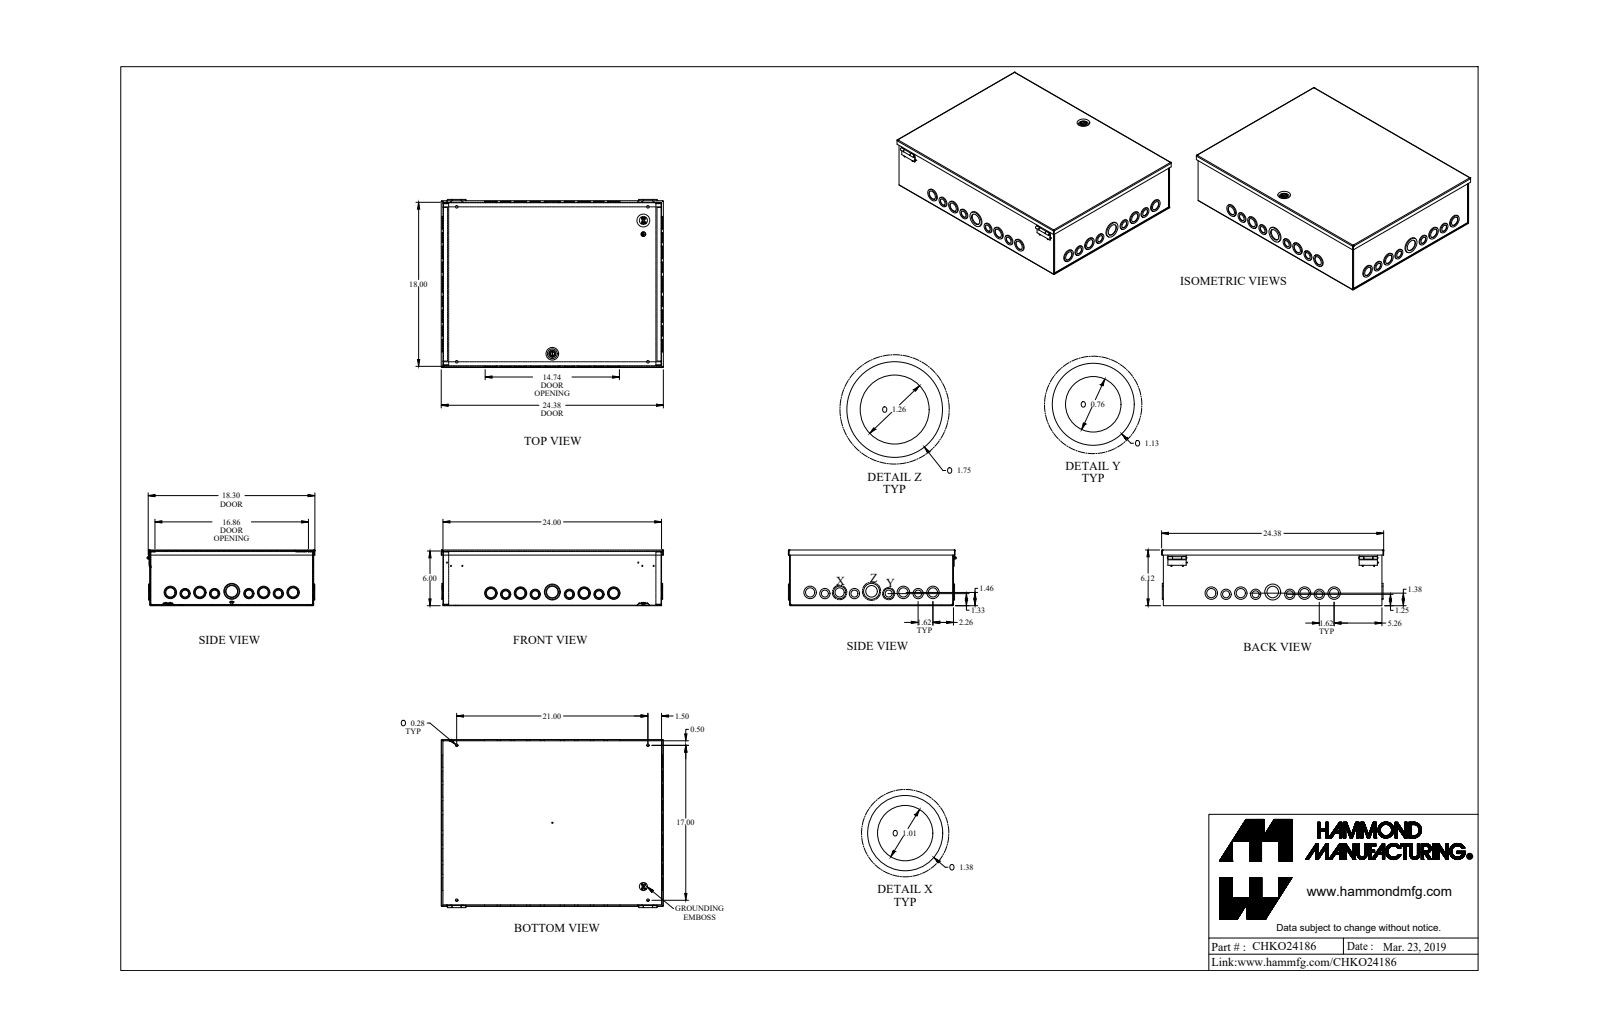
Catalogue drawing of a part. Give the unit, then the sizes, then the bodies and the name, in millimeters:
Units: millimetres
Overall size (bounding box): 619.3 × 468.5 × 155.4
Round holes (diameter × count): ⌀25.7 ×16, ⌀32 ×10, ⌀19.3 ×8, ⌀7.1 ×4, ⌀41.6 ×2, ⌀3.2 ×1, ⌀4.3 ×1, ⌀8.1 ×1, ⌀12.1 ×1, ⌀12.7 ×1
Round bosses / shafts (diameter × count): ⌀28.6 ×14, ⌀34.9 ×9, ⌀3.3 ×8, ⌀22.2 ×6, ⌀28.6 ×4, ⌀22.2 ×4, ⌀34.9 ×3, ⌀44.5 ×2
Partial cylindrical surfaces — rounded edges, fillets, slot ends (radius × count): R0.7 ×16, R2.2 ×16, R1.4 ×8, R0.3 ×4, R2.5 ×4, R0.9 ×2, R2 ×2, R6.4 ×2
Main face-to-face distances: 1.4, 153.9, 155.4, 152.5, 455.8, 608.2, 457.2, 454.3, 609.6, 606.7
Hole centre spacings: 41.3, 82.3, 219, 177.8, 260.1, 48.2, 89, 123.5
Volume: 1 421 000 mm³ · Surface area: 1 970 000 mm²
Bodies: 12 solids, 919 faces (416 planar, 460 cylindrical, 43 other)
Part name (STEP PRODUCT): CHKO24186_Default
STEP written by: SolidWorks 2019 (CONFIG_CONTROL_DESIGN)
